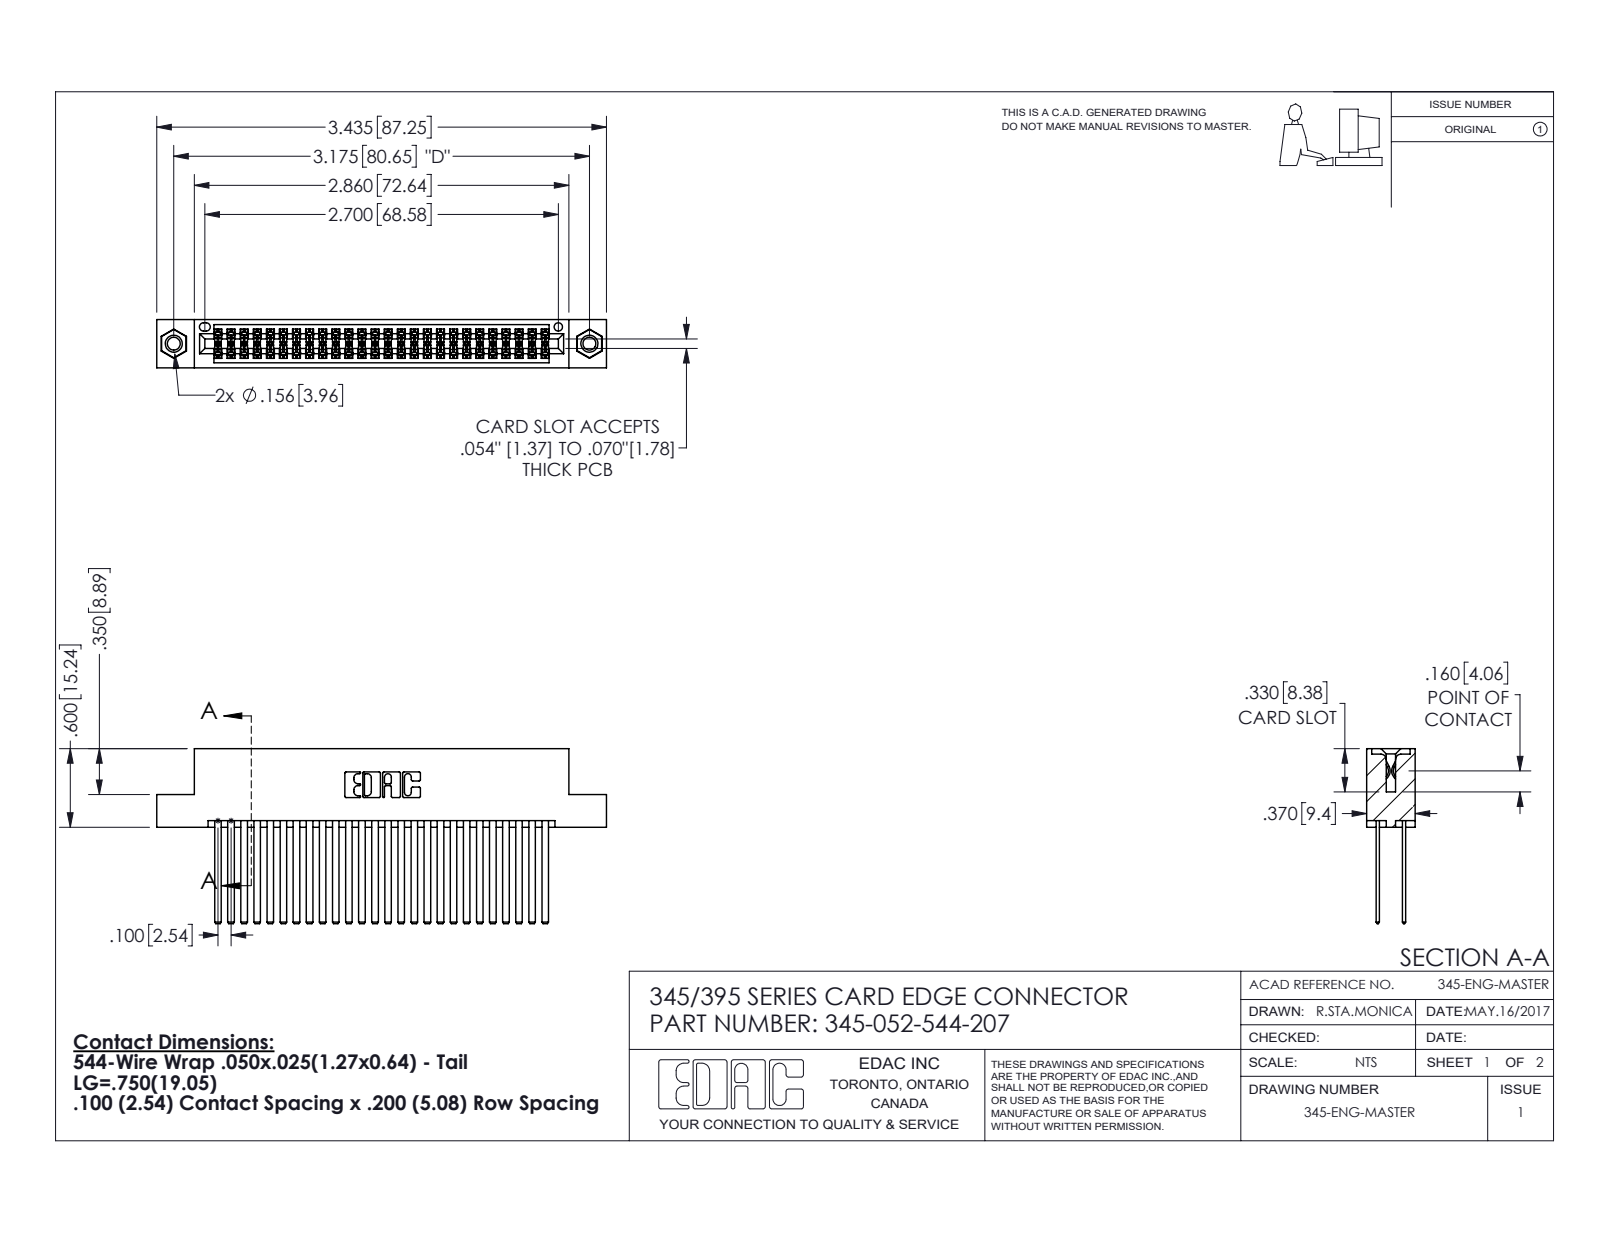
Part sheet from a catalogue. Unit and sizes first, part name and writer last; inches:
Units: inches
Overall size (bounding box): 3.435 × 1.337 × 0.37
Round holes (diameter × count): ⌀0.098 ×2, ⌀0.125 ×2, ⌀0.156 ×2, ⌀0.064 ×1
Round bosses / shafts (diameter × count): ⌀0.155 ×2
Partial cylindrical surfaces — rounded edges, fillets, slot ends (radius × count): R0.006 ×78, R0.01 ×22, R0.007 ×6, R0.031 ×6, R0.026 ×3, R0.014 ×2, R0.019 ×2, R0.022 ×2
Main face-to-face distances: 0.2, 0.072, 0.298, 0.025, 0.098, 0.272, 0.225, 0.175, 0.37, 0.05
Hole centre spacings: 0.27, 2.94, 3.175
Volume: 0.552 in³ · Surface area: 23.59 in²
Bodies: 55 solids, 2474 faces (1620 planar, 838 cylindrical, 16 other)
Part name (STEP PRODUCT): 345-292-001_345-293-144; 345-250-001_345-250-005-103; 345-052-544-207; 345 Part_Flush Mounting Lugs - 0.156 Dia-TI
STEP written by: SolidWorks 2016 (CONFIG_CONTROL_DESIGN)
